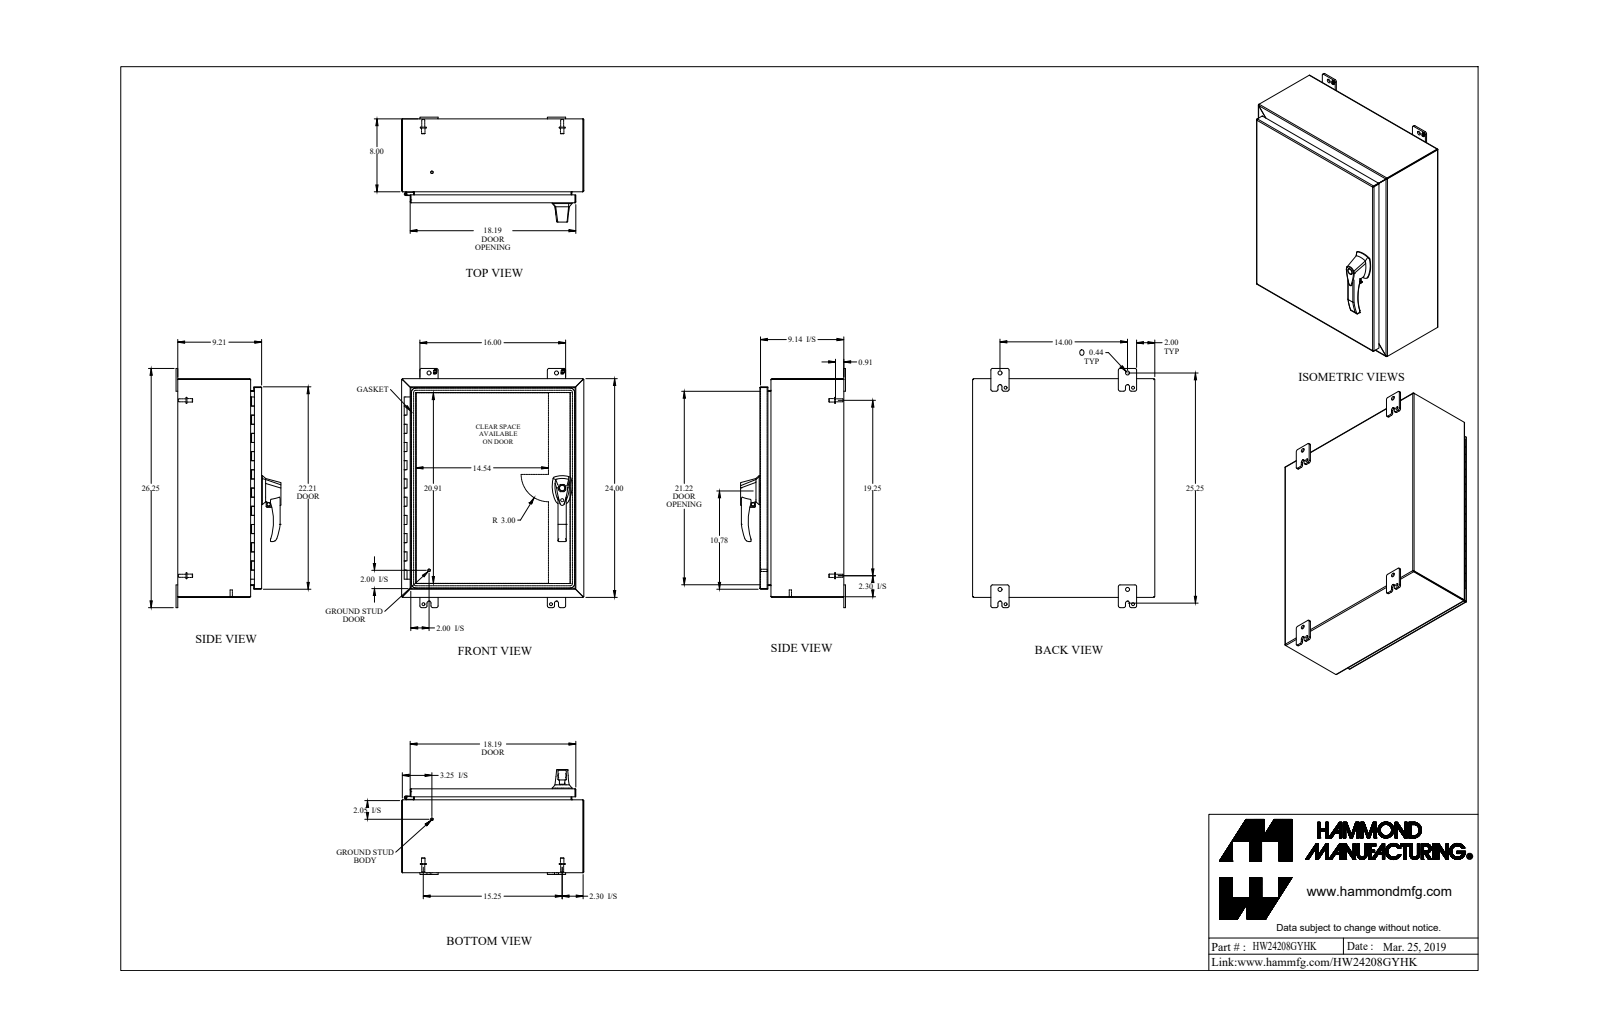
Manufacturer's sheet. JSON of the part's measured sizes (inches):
{"part_name": "HW24208GYHK", "step_written_by": "SolidWorks 2018 (AUTOMOTIVE_DESIGN)", "units": "inches", "bodies": {"solids": 43, "faces": 1366, "planar": 668, "cylindrical": 553, "other": 145}, "overall_size": [26.25, 20, 11.512], "volume_in3": 168.6, "surface_area_in2": 4260, "round_holes": [[0.176, 6], [0.313, 4], [0.25, 3], [0.265, 3], [0.413, 3], [0.196, 2], [0.256, 2], [0.394, 2], [0.437, 2], [0.187, 1], [0.233, 1], [0.334, 1]], "round_bosses_or_shafts": [[0.375, 9], [0.25, 7], [0.156, 6], [0.65, 4], [0.33, 4], [1, 3], [0.63, 2], [0.51, 2]], "partial_cylinders_radius": [[0.25, 27], [0.188, 24], [0.036, 20], [0.108, 20], [0.06, 12], [0.125, 9], [0.045, 8], [0.218, 8]], "face_to_face_distances": [0.072, 0.072, 9.138, 9.066, 9.21, 9.138, 19.928, 23.928, 7.928, 19.856], "hole_center_spacings": [8.118, 8.119, 16.237, 1.111, 7.877, 8.119, 14, 19.224]}
